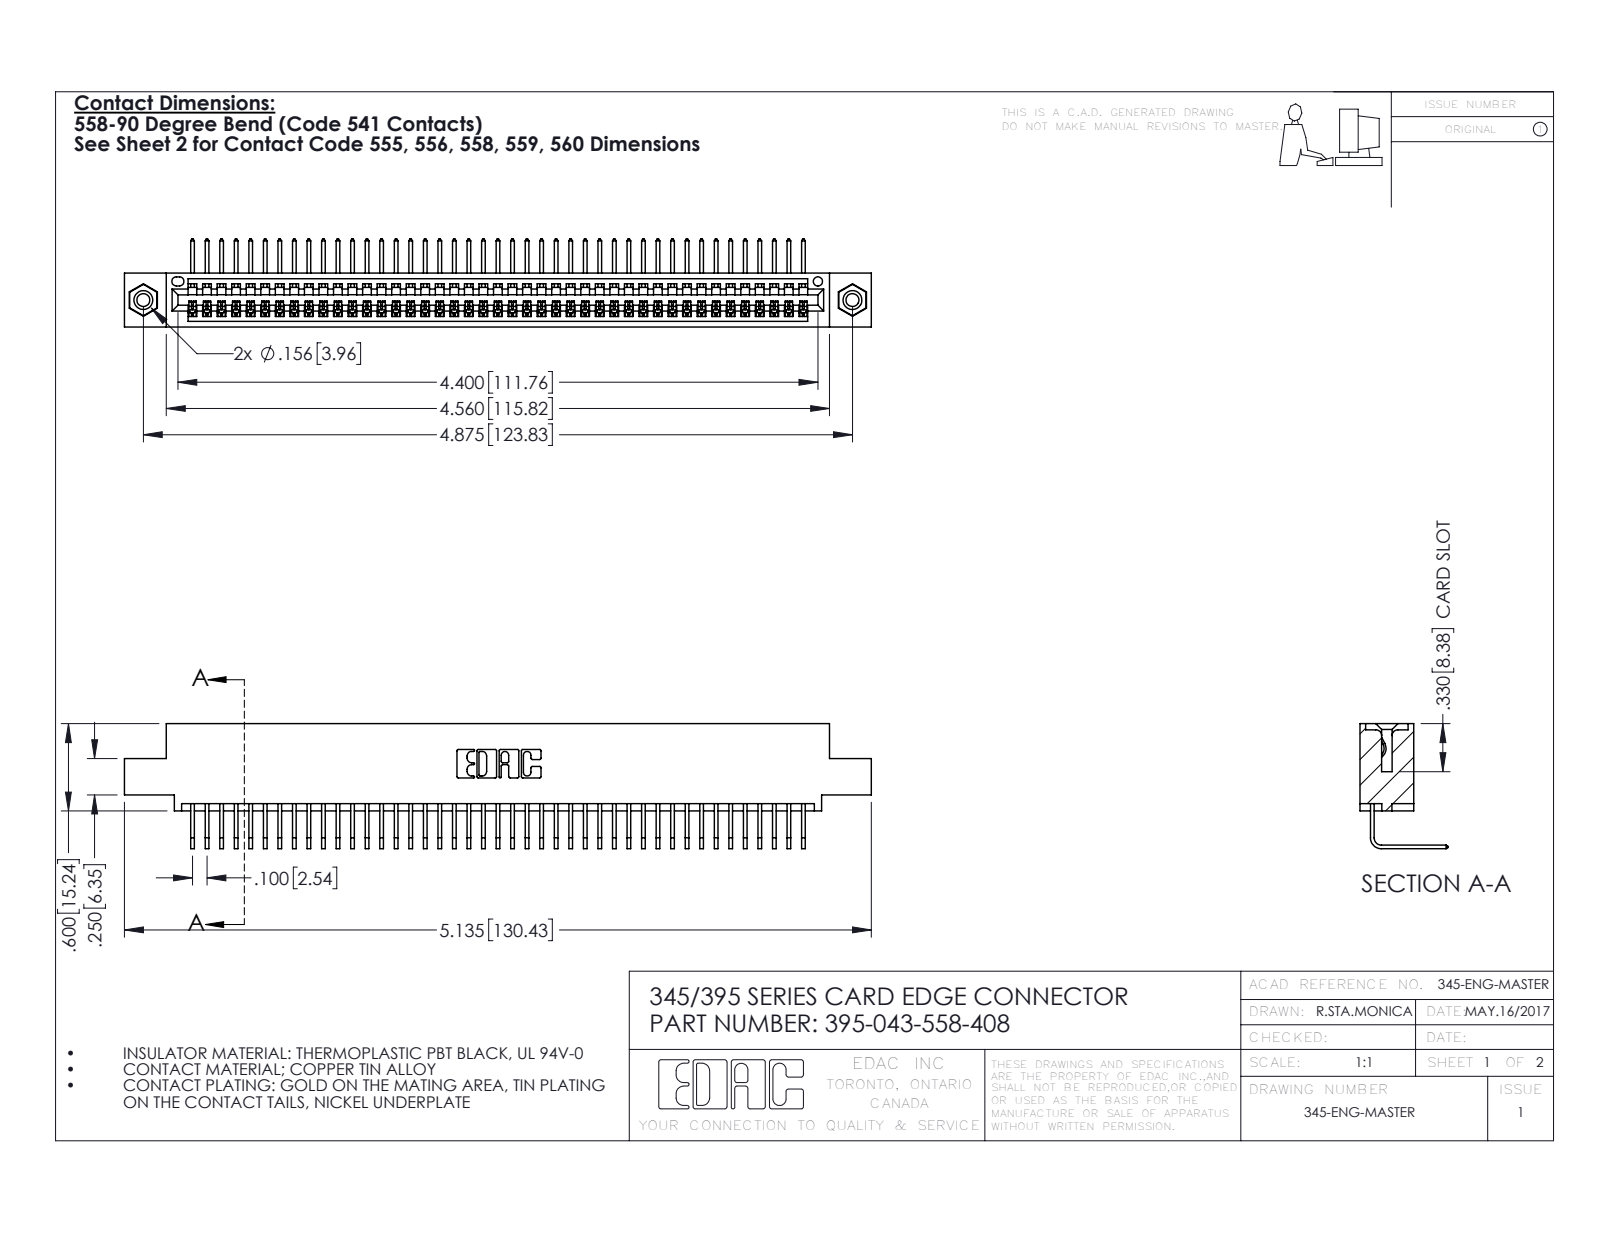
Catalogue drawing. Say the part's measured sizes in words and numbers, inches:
The part is named "345-250-001_345-250-003-102; 345 Part_0.110 Offset - 0.156 Dia-TI; 345-292-001_558 Tail - 2; 395-043-558-408". Its 3-D file was written by "SolidWorks 2016 (CONFIG_CONTROL_DESIGN)". It is 46 solids with 2770 faces: 1922 planar, 832 cylindrical and 16 other. Overall it measures 5.135 by 0.859 by 0.605 inches. Its volume is 0.76 cubic inches and its surface area 27.15 square inches. Round holes: 2 of diameter 0.089, 2 of diameter 0.125, 2 of diameter 0.156, 1 of diameter 0.064. Round bosses or shafts: 2 of diameter 0.155. Partial cylindrical surfaces (rounded edges, fillets, slot ends): 86 of radius 0.006, 22 of radius 0.01, 6 of radius 0.007, 6 of radius 0.031, 3 of radius 0.026, 2 of radius 0.031, 2 of radius 0.04, 1 of radius 0.014. The main face-to-face distances are 0.072, 0.298, 0.37, 0.2, 0.098, 0.272, 0.025, 0.225, 0.149, 0.072. The hole center spacings are 0.27, 4.639, 4.875.
